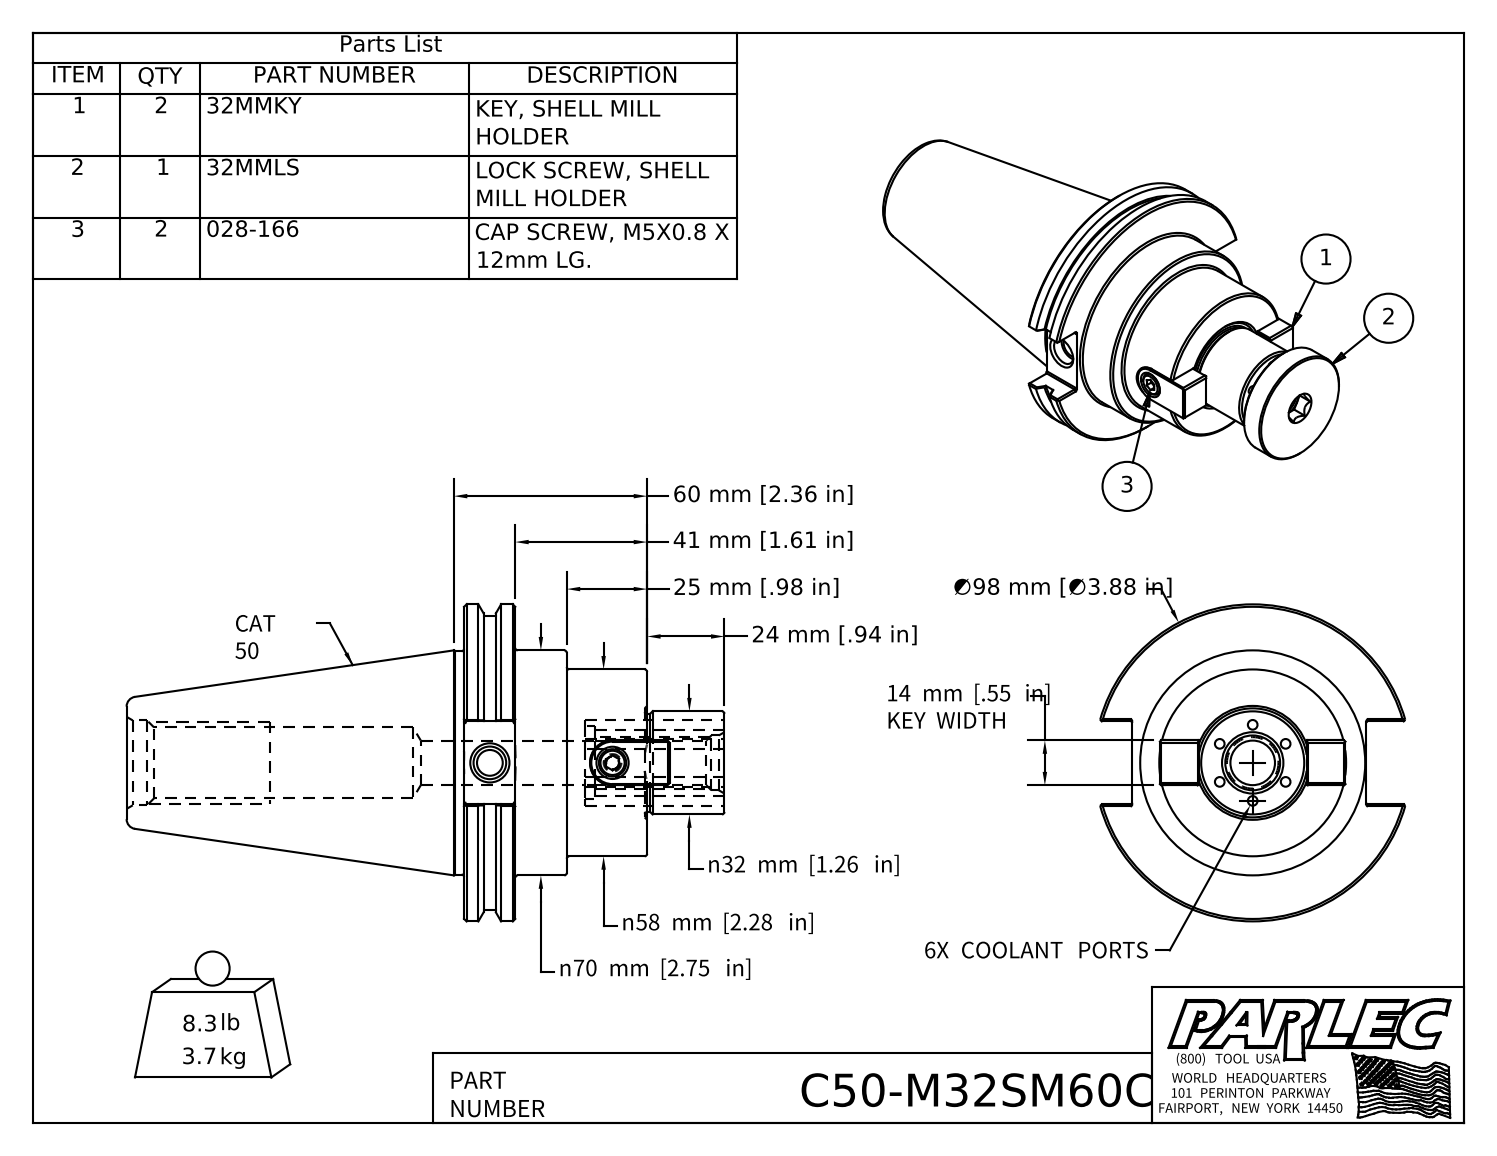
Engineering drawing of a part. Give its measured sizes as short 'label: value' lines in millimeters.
name: C50-M32SM60C; 32MMKY; 028-166; 32MMLS
written by: Autodesk Inventor 2022 (AUTOMOTIVE_DESIGN)
unit: mm
bodies: 6 solids, 216 faces (106 planar, 59 cylindrical, 51 other)
size: 200.9 × 98.4 × 94.7
volume: 476 700 mm³; area: 70 060 mm²
holes: 6× ⌀3, 1× ⌀4.1, 1× ⌀5.5, 1× ⌀8, 1× ⌀10, 1× ⌀10, 1× ⌀10.1, 1× ⌀13.8, 1× ⌀17, 1× ⌀22, 1× ⌀26.4
bosses: 1× ⌀98.4, 1× ⌀91.3, 1× ⌀69.9, 1× ⌀69.3, 1× ⌀58, 1× ⌀42, 1× ⌀32, 1× ⌀30.5
rounds: 12× R0.5, 1× R7, 1× R7, 1× R11.4
face distances: 15.9, 56.8, 40.9, 80.3, 96.2, 39.3, 87.2, 71.3, 30.4, 9
hole spacings: 11.8, 20.5, 11.8, 23.6, 23.6, 38.1
